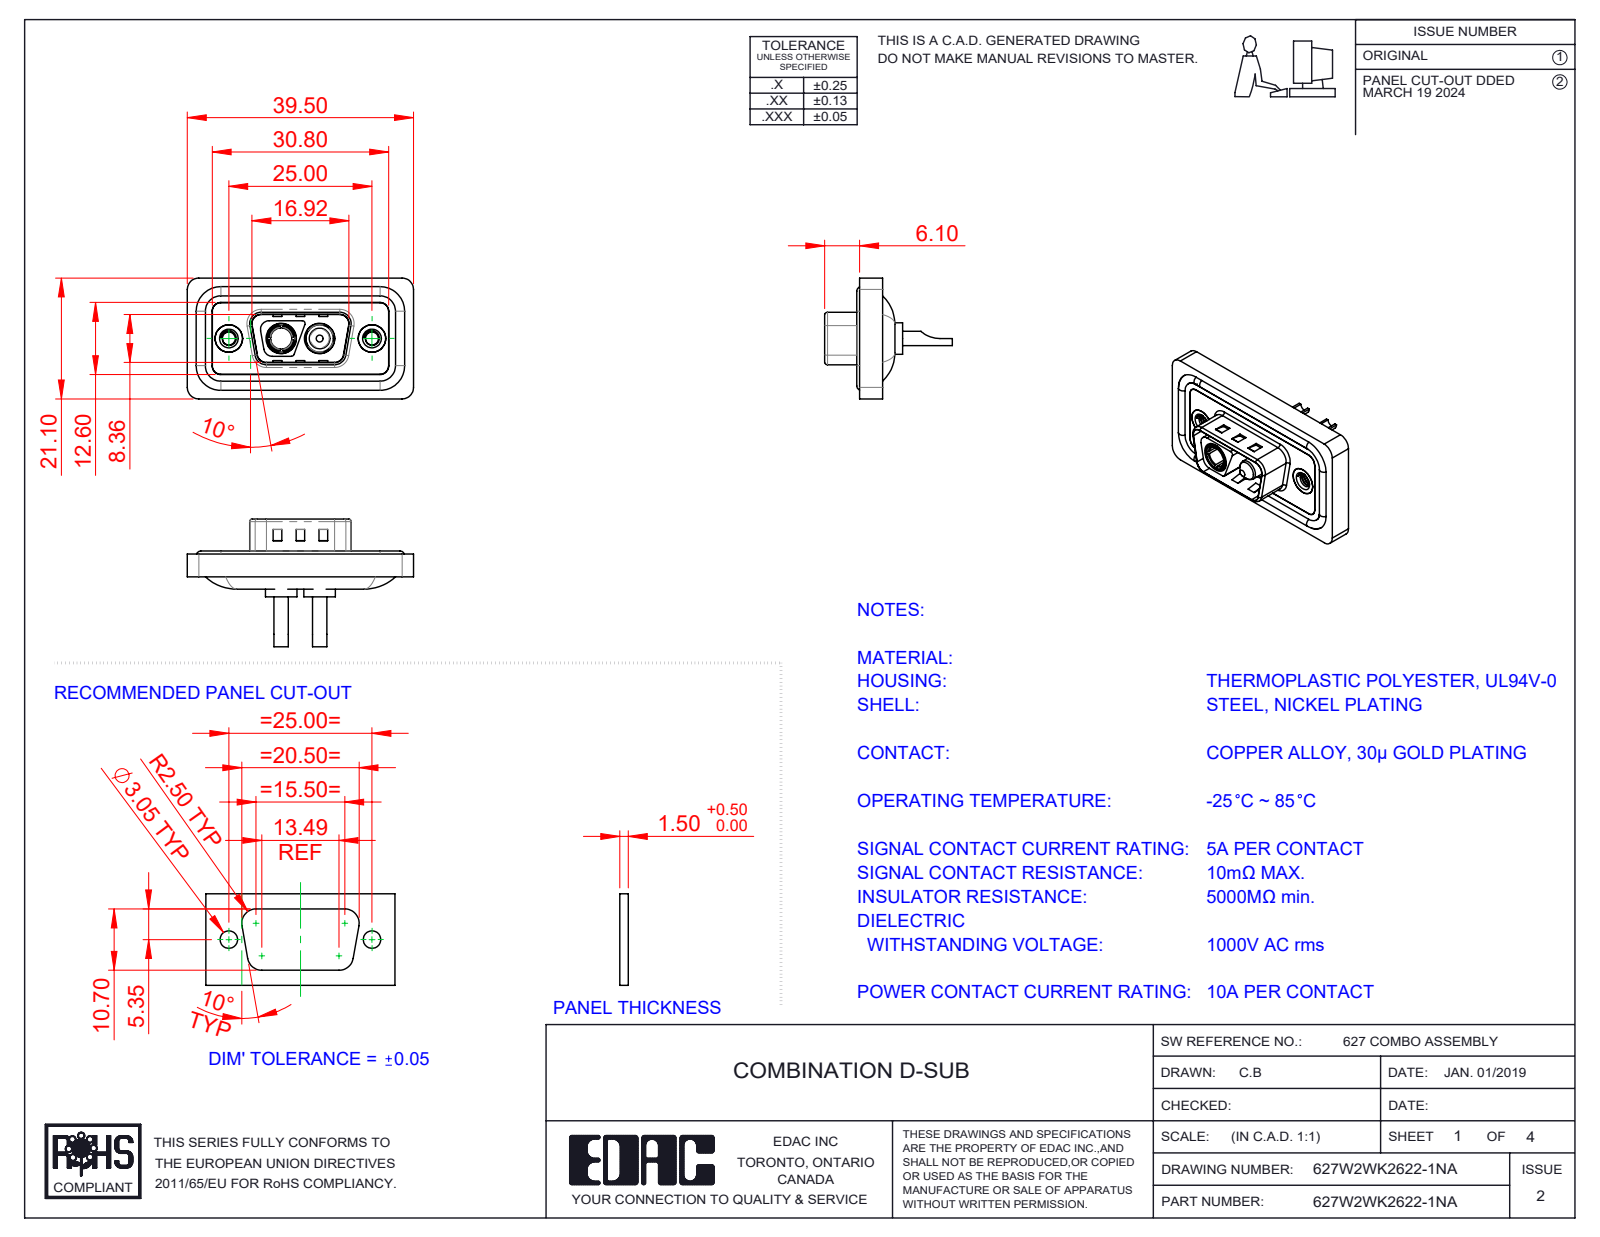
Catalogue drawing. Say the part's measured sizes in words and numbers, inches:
The part is named "627Combo Waterproof Housing_09 Contacts; 627Combo Shell Rear_09 Contacts; Power Pin_10A SC; 627Combo Threaded Rivet_A (+4 more)". Its 3-D file was written by "SolidWorks 2023 (CONFIG_CONTROL_DESIGN)". It is 11 solids with 544 faces: 193 planar, 235 cylindrical and 116 other. Overall it measures 1.555 by 0.878 by 0.831 inches. Its volume is 0.278 cubic inches and its surface area 11.52 square inches. Round holes: 2 of diameter 0.067, 2 of diameter 0.089, 2 of diameter 0.157, 2 of diameter 0.189, 2 of diameter 0.191, 2 of diameter 0.197, 2 of diameter 0.209, 1 of diameter 0.146. Round bosses or shafts: 4 of diameter 0.063, 2 of diameter 0.217, 2 of diameter 0.205, 2 of diameter 0.193, 2 of diameter 0.187, 2 of diameter 0.148, 2 of diameter 0.098, 1 of diameter 0.195. Partial cylindrical surfaces (rounded edges, fillets, slot ends): 24 of radius 0.059, 18 of radius 0.079, 10 of radius 0.02, 8 of radius 0.063, 4 of radius 0.01, 4 of radius 0.024, 4 of radius 0.026, 4 of radius 0.035. The main face-to-face distances are 0.016, 0.043, 0.114, 0.02, 0.122, 0.063, 0.059, 0.157, 0.098, 0.071. The hole center spacings are 0.36, 0.624, 0.265, 0.984.
